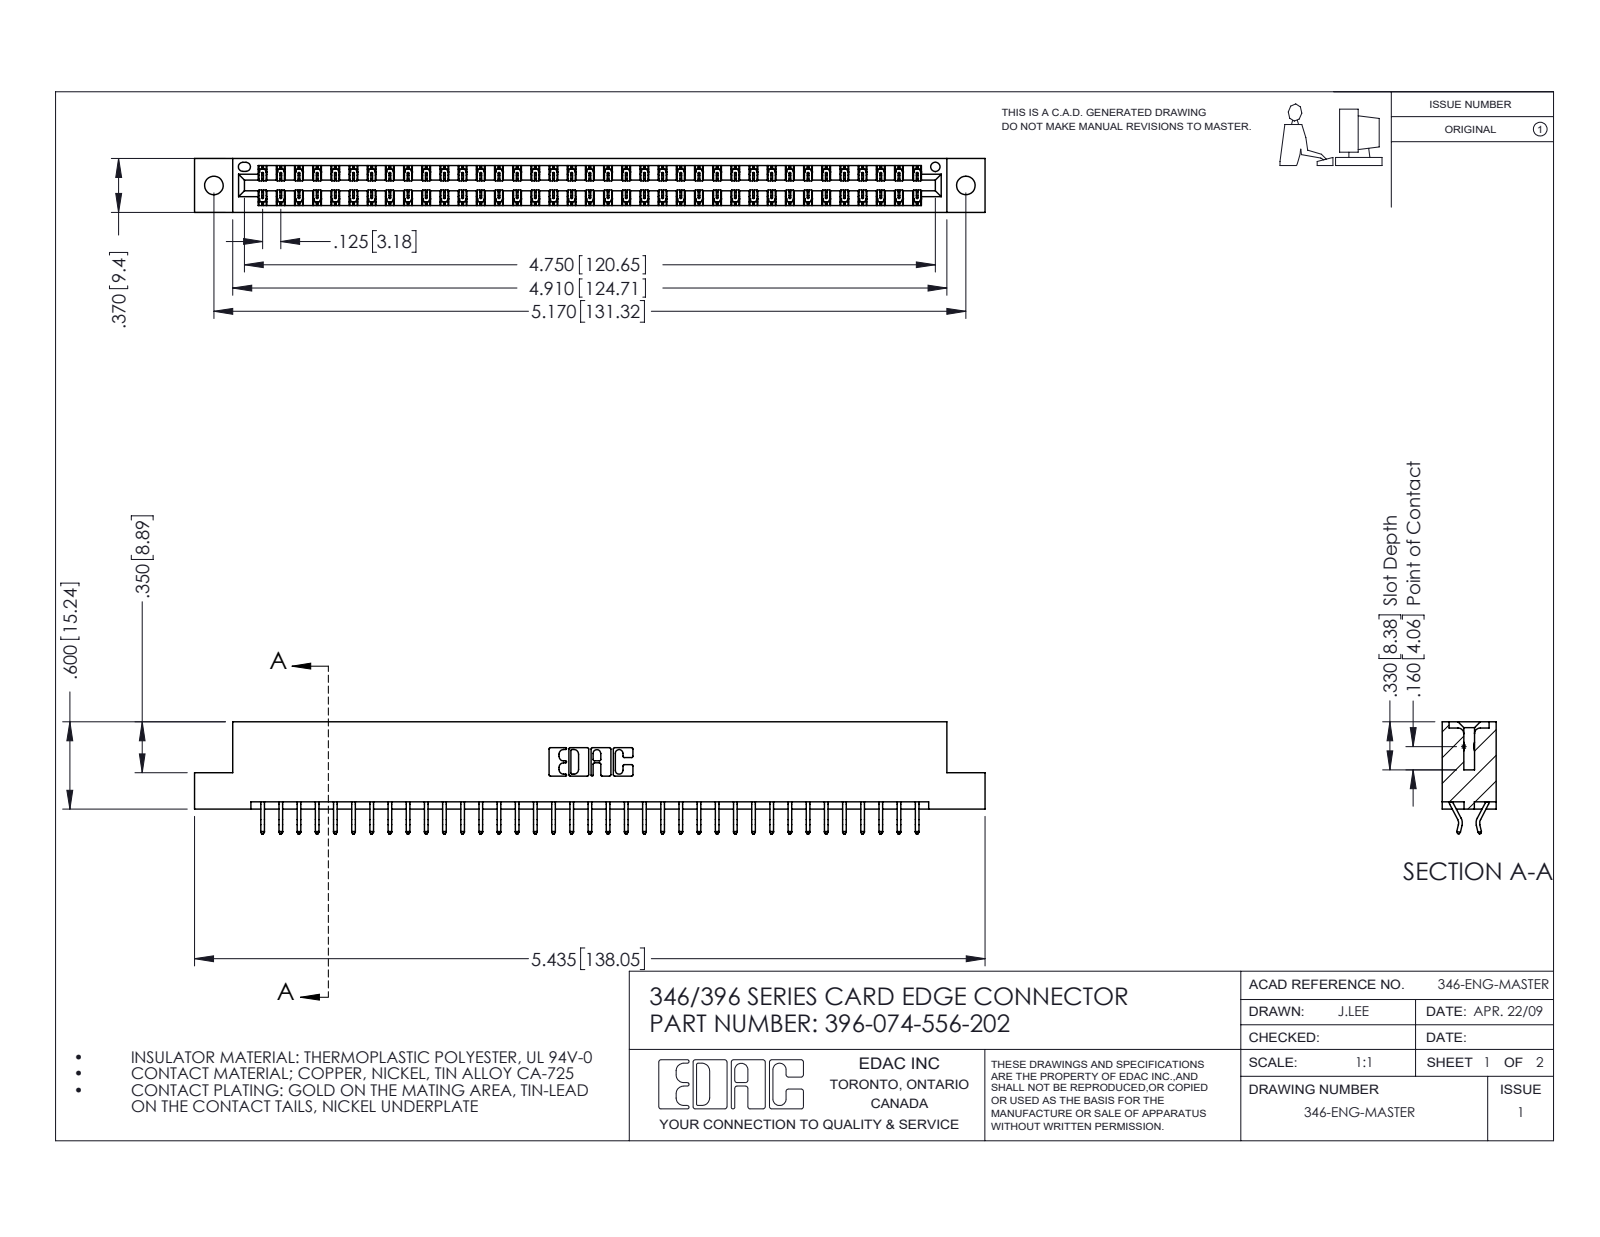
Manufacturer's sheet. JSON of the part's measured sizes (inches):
{"part_name": "345-292-001_556 Tail; 396-074-556-202; 346 Part_Flush Mounting Lugs - 0.128 Dia", "step_written_by": "SolidWorks 2016 (CONFIG_CONTROL_DESIGN)", "units": "inches", "bodies": {"solids": 75, "faces": 4414, "planar": 2962, "cylindrical": 1452, "other": 0}, "overall_size": [5.435, 0.77, 0.37], "volume_in3": 0.817, "surface_area_in2": 27.87, "round_holes": [[0.128, 2], [0.064, 1]], "partial_cylinders_radius": [[0.006, 111], [0.01, 22], [0.007, 6], [0.031, 6], [0.026, 3], [0.01, 2], [0.014, 2], [0.022, 2]], "face_to_face_distances": [0.048, 0.322, 0.37, 0.25, 0.025, 0.072, 0.298, 0.275, 0.148, 0.222], "hole_center_spacings": [0.246, 4.961, 5.17]}
